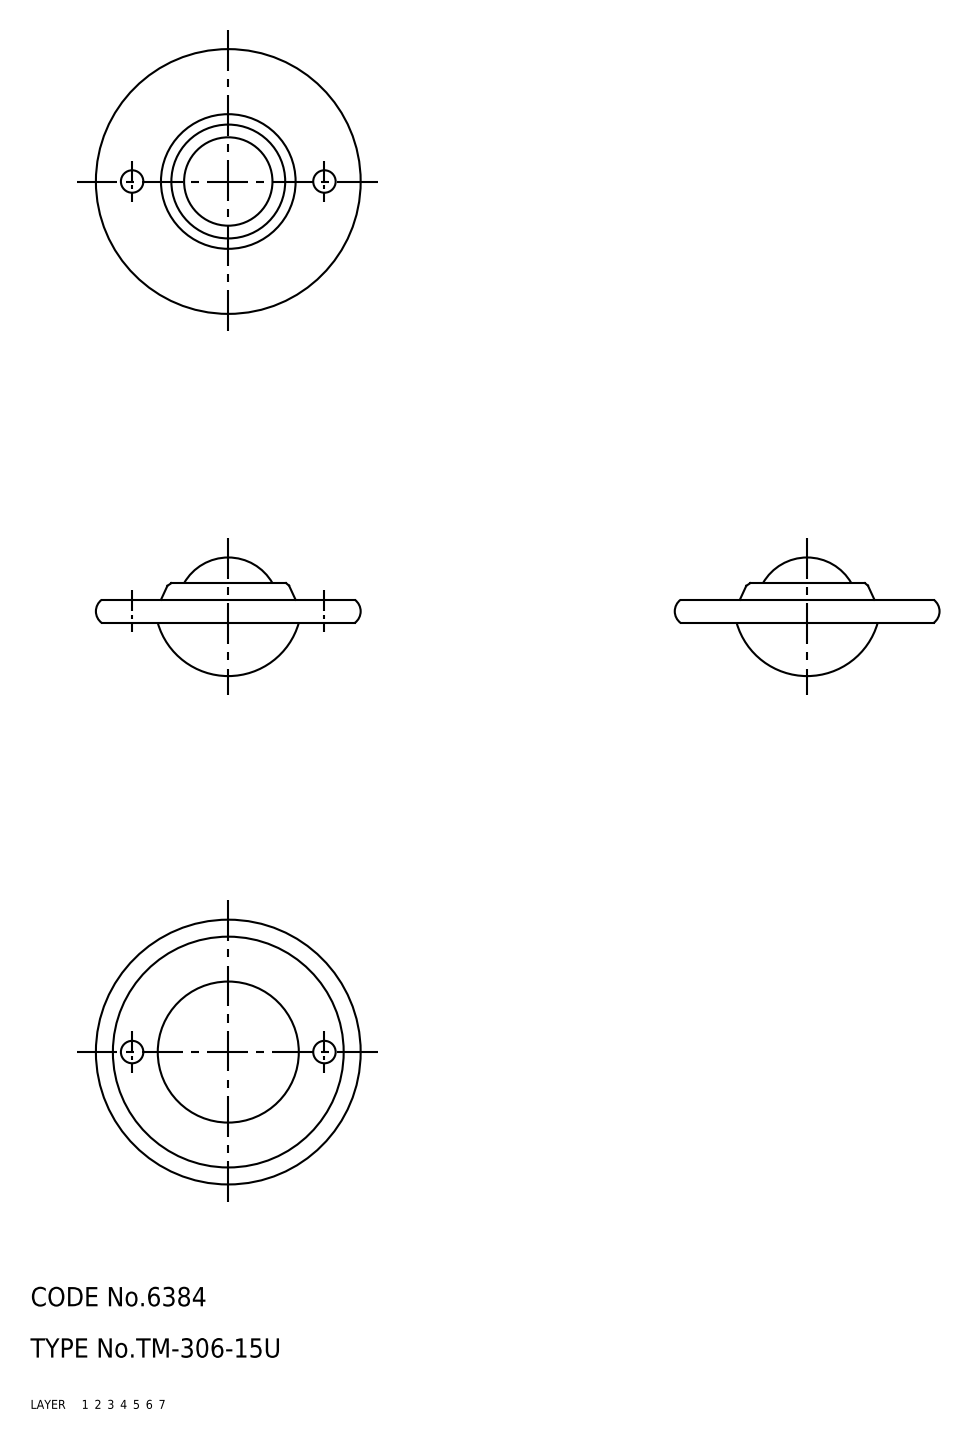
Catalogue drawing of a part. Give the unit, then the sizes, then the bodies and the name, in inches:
Units: inches
Overall size (bounding box): 1.626 × 1.626 × 0.728
Volume: 0.354 in³ · Surface area: 11.27 in²
Bodies: 3 solids, 40 faces (0 planar, 0 cylindrical, 40 other)
Part name (STEP PRODUCT): 67112503; 67112516; 67112529
STEP written by: CADfix (AUTOMOTIVE_DESIGN)
